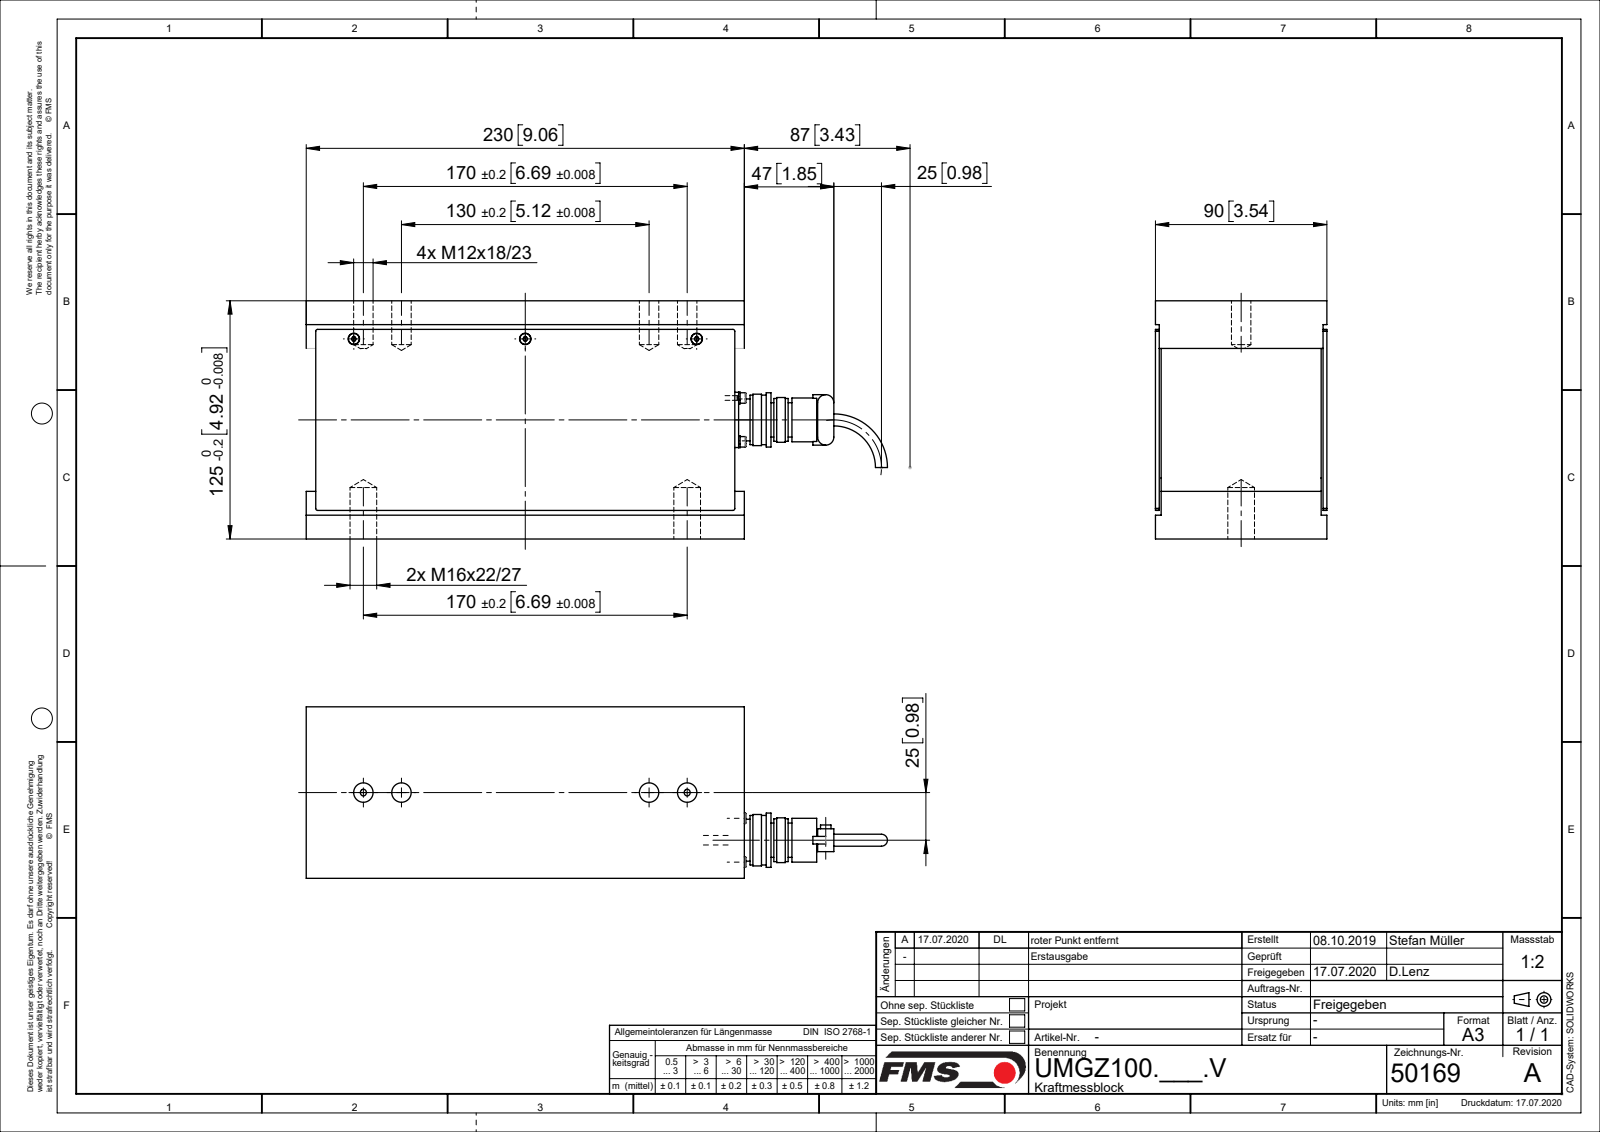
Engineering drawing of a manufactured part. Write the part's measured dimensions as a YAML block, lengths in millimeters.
part_name: "U50169; U4787104; TEIL1; U47671 (+5 more)"
step_written_by: "Mechanical Desktop 2007 (CONFIG_CONTROL_DESIGN)"
units: millimeters
bodies: {solids: 18, faces: 383, planar: 133, cylindrical: 160, other: 90}
overall_size: [327.5, 125, 90]
volume: 2483000
surface_area: 229000
round_holes:
  - {diameter: 2.6, count: 7}
  - {diameter: 3.2, count: 4}
  - {diameter: 10.68, count: 4}
  - {diameter: 3.4, count: 3}
  - {diameter: 6, count: 3}
  - {diameter: 14.68, count: 2}
round_bosses_or_shafts:
  - {diameter: 3, count: 7}
  - {diameter: 6.2, count: 4}
  - {diameter: 5.5, count: 4}
  - {diameter: 2.5, count: 4}
  - {diameter: 28, count: 1}
  - {diameter: 23, count: 1}
  - {diameter: 22, count: 1}
  - {diameter: 21, count: 1}
partial_cylinders:
  - {radius: 4, count: 4}
face_to_face_distances: [2, 88, 85, 3, 1, 87, 90, 86, 125, 84]
hole_center_spacings: [23, 20, 32.53, 90, 150, 130, 170, 180]
